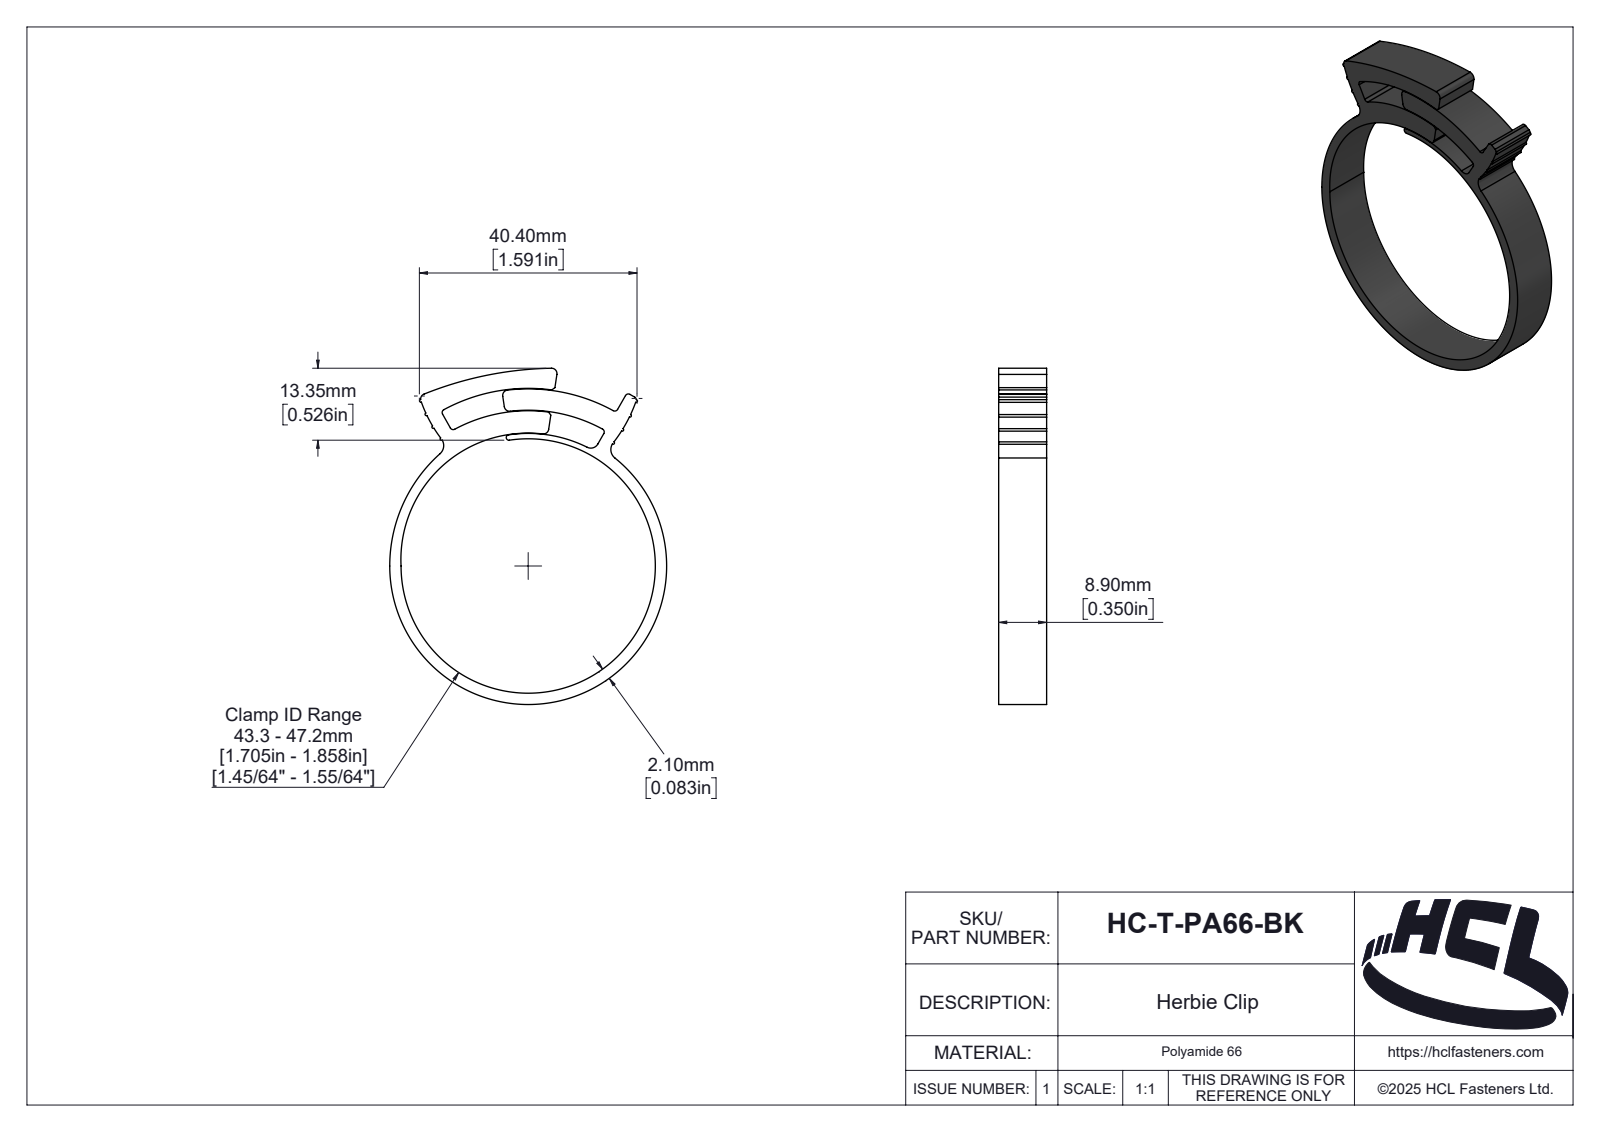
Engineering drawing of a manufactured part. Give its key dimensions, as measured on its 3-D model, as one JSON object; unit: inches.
{"part_name": "HC-T-PA66-BK", "step_written_by": "SolidWorks 2025 (AUTOMOTIVE_DESIGN)", "units": "inches", "bodies": {"solids": 1, "faces": 162, "planar": 13, "cylindrical": 100, "other": 49}, "overall_size": [2.456, 2.024, 0.35], "volume_in3": 0.314, "surface_area_in2": 8.133, "partial_cylinders_radius": [[0.01, 8], [0.024, 6], [0.039, 5], [0.079, 2], [0.007, 1], [0.02, 1], [0.026, 1], [0.033, 1]], "face_to_face_distances": [0.35]}
